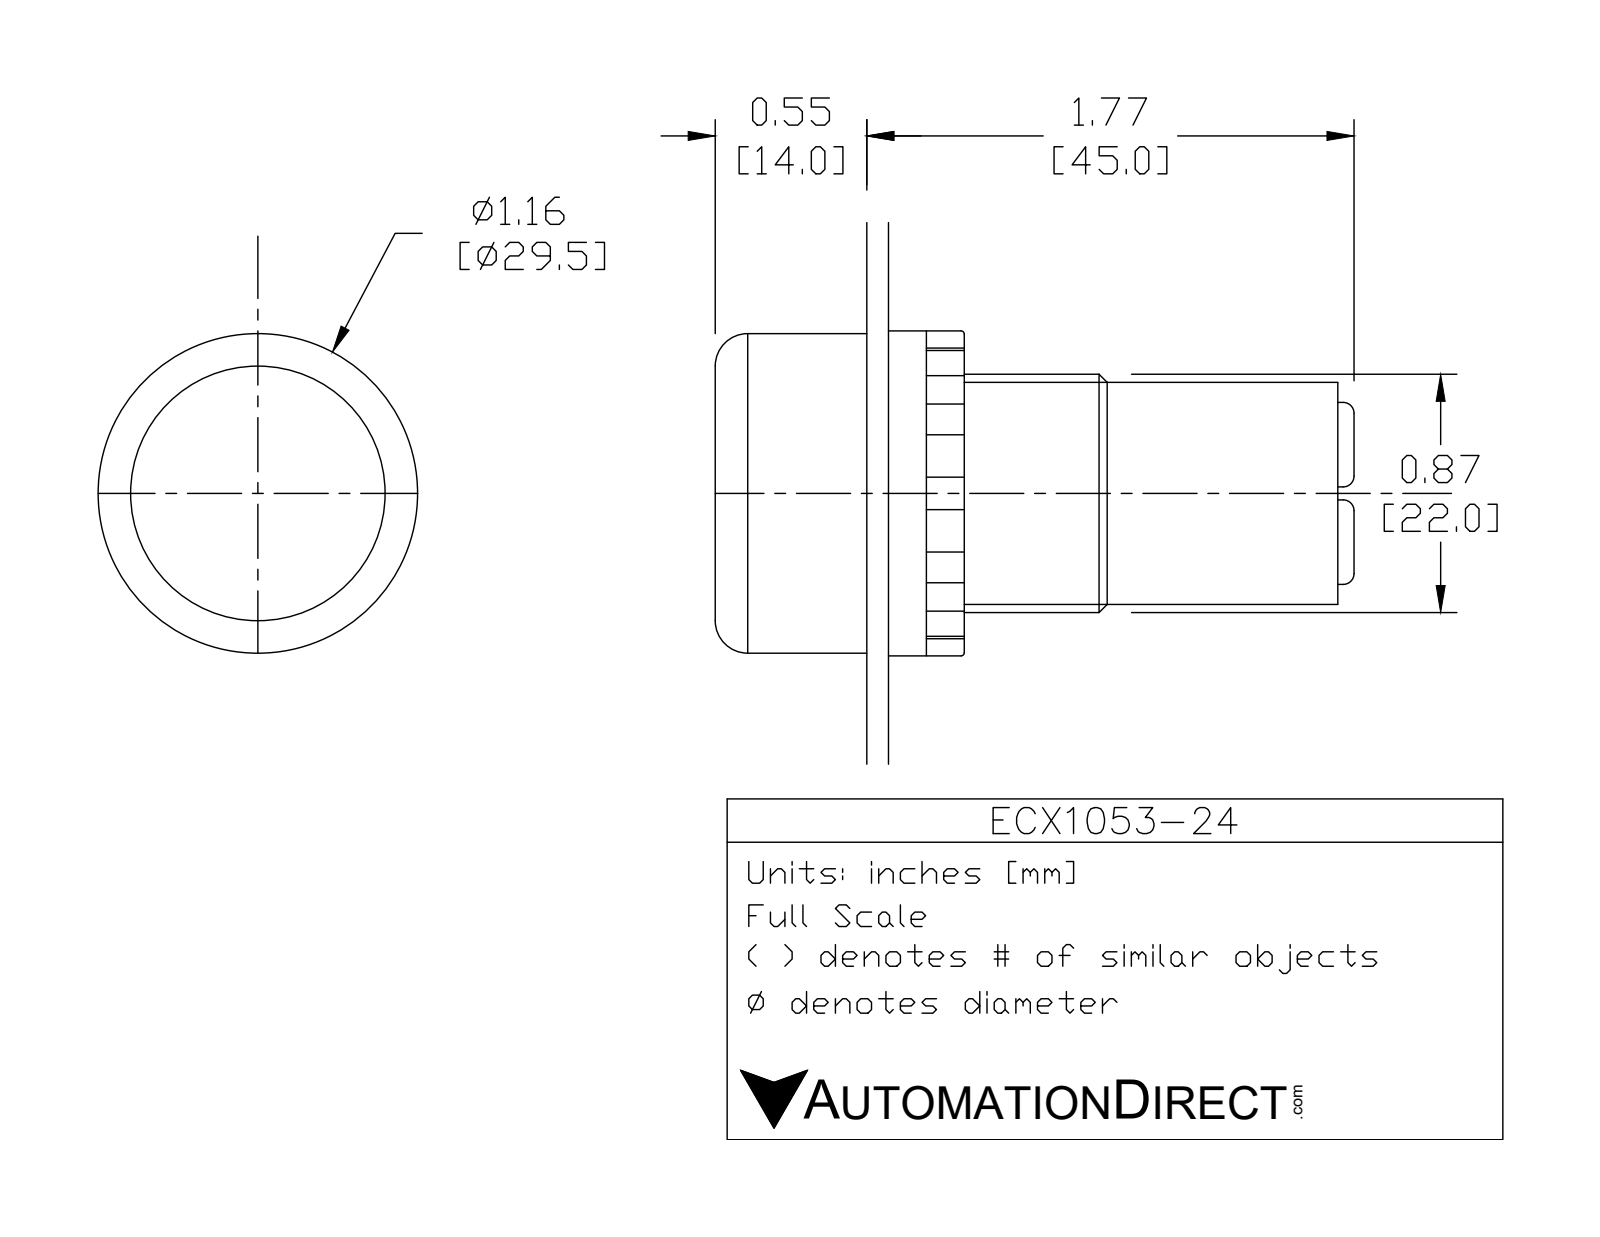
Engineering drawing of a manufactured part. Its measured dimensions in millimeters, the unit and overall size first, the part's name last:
Units: millimetres
Overall size (bounding box): 59 × 30 × 30
Round holes (diameter × count): ⌀5.5 ×2, ⌀22.5 ×1
Round bosses / shafts (diameter × count): ⌀4 ×2, ⌀30 ×1, ⌀29 ×1, ⌀26.5 ×1, ⌀22 ×1, ⌀20 ×1
Partial cylindrical surfaces — rounded edges, fillets, slot ends (radius × count): R1 ×12, R9 ×1
Main face-to-face distances: 13.5, 0.5, 14, 20, 6, 6.5, 39, 7, 13, 27
Hole centre spacings: 4.62, 9.24
Volume: 26 294 mm³ · Surface area: 9 700 mm²
Bodies: 6 solids, 125 faces (63 planar, 41 cylindrical, 21 other)
Part name (STEP PRODUCT): ECX1053-24
STEP written by: SolidWorks 2017 (AUTOMOTIVE_DESIGN)
